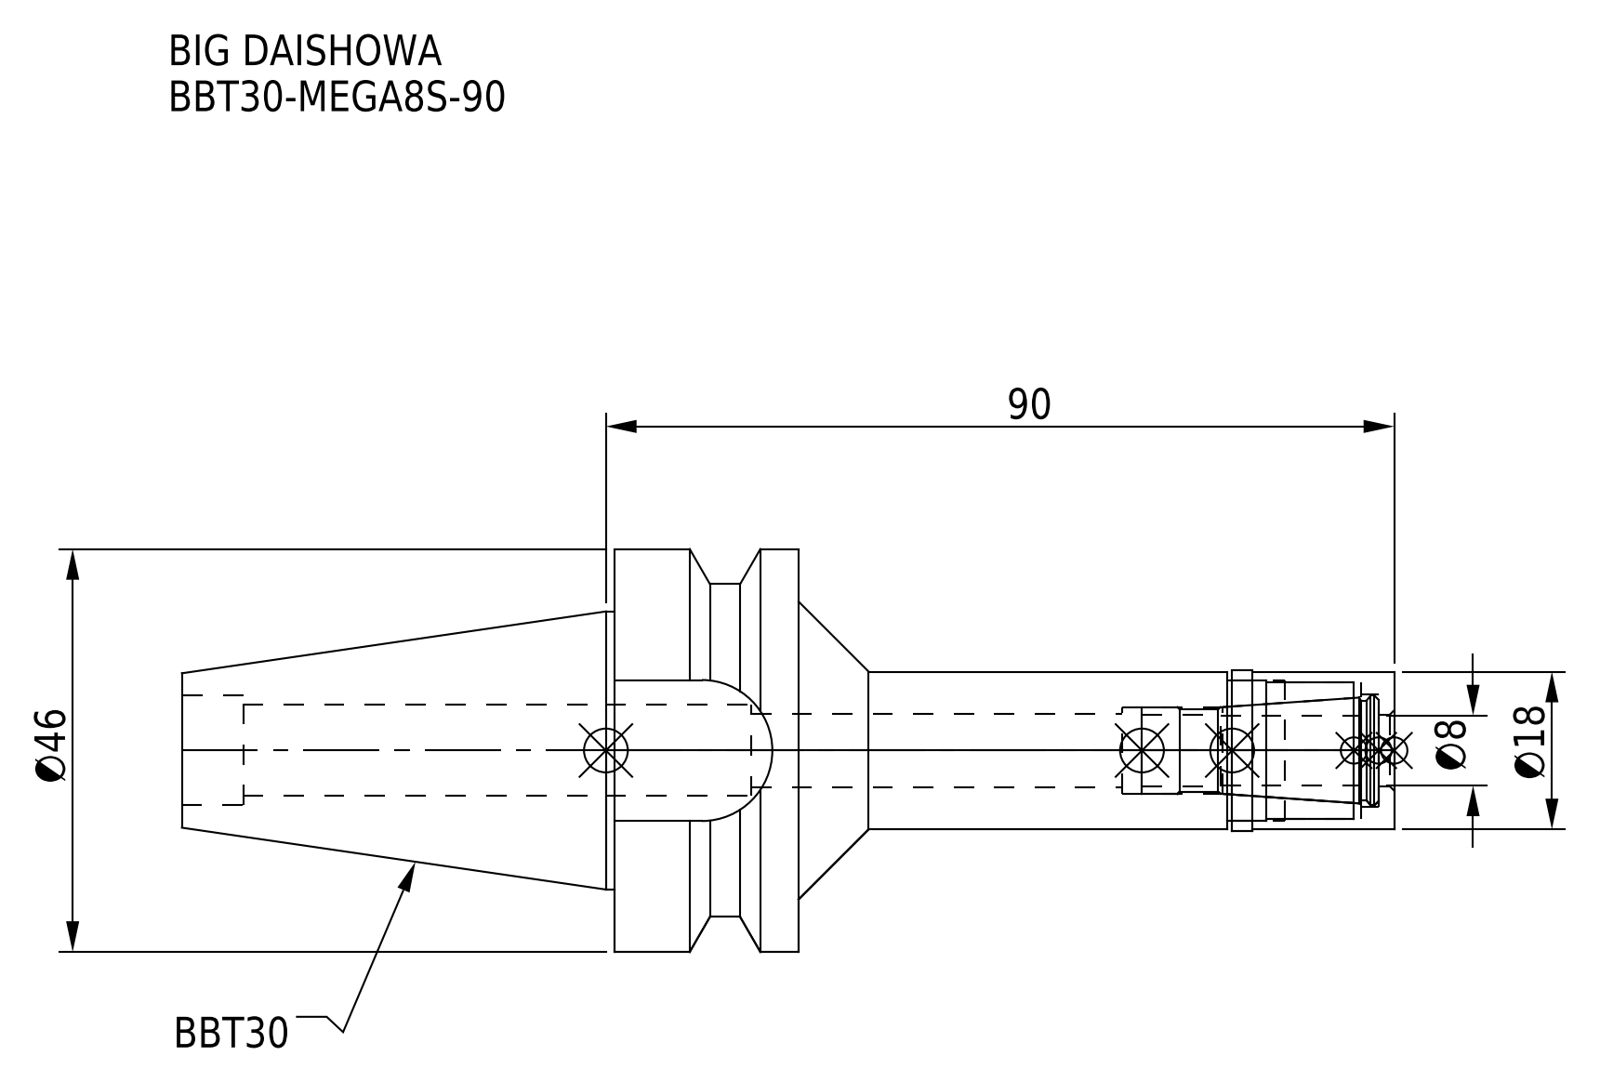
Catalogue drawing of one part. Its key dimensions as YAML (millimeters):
part_name: "DXF_TEMP_ASSY_ASM_4_ASM.stp; BBT30-MEGA8S-90_1.stp; BBT30MS08090-080_ASM.stp; BBT30-MEGA8S-90-080-FreeParts (+3 more)"
step_written_by: "SolidWorks 2019 (CONFIG_CONTROL_DESIGN)"
units: millimeters
bodies: {solids: 2, faces: 71, planar: 21, cylindrical: 38, other: 12}
overall_size: [138.4, 46, 46]
volume: 62508
surface_area: 19866
round_holes:
  - {diameter: 8.2, count: 1}
  - {diameter: 8.4, count: 1}
  - {diameter: 9.9, count: 1}
  - {diameter: 10.4, count: 1}
  - {diameter: 12.5, count: 1}
  - {diameter: 12.9, count: 1}
  - {diameter: 15.6, count: 1}
  - {diameter: 16.1, count: 1}
round_bosses_or_shafts:
  - {diameter: 46, count: 1}
  - {diameter: 31.75, count: 1}
  - {diameter: 18.3, count: 1}
  - {diameter: 18, count: 1}
  - {diameter: 18, count: 1}
  - {diameter: 16.1, count: 1}
  - {diameter: 15.6, count: 1}
partial_cylinders:
  - {radius: 8.05, count: 1}
  - {radius: 19, count: 1}
face_to_face_distances: [21, 32.6, 68, 89, 138.4, 70.4, 49.4, 63.4, 16.1, 4.6]
